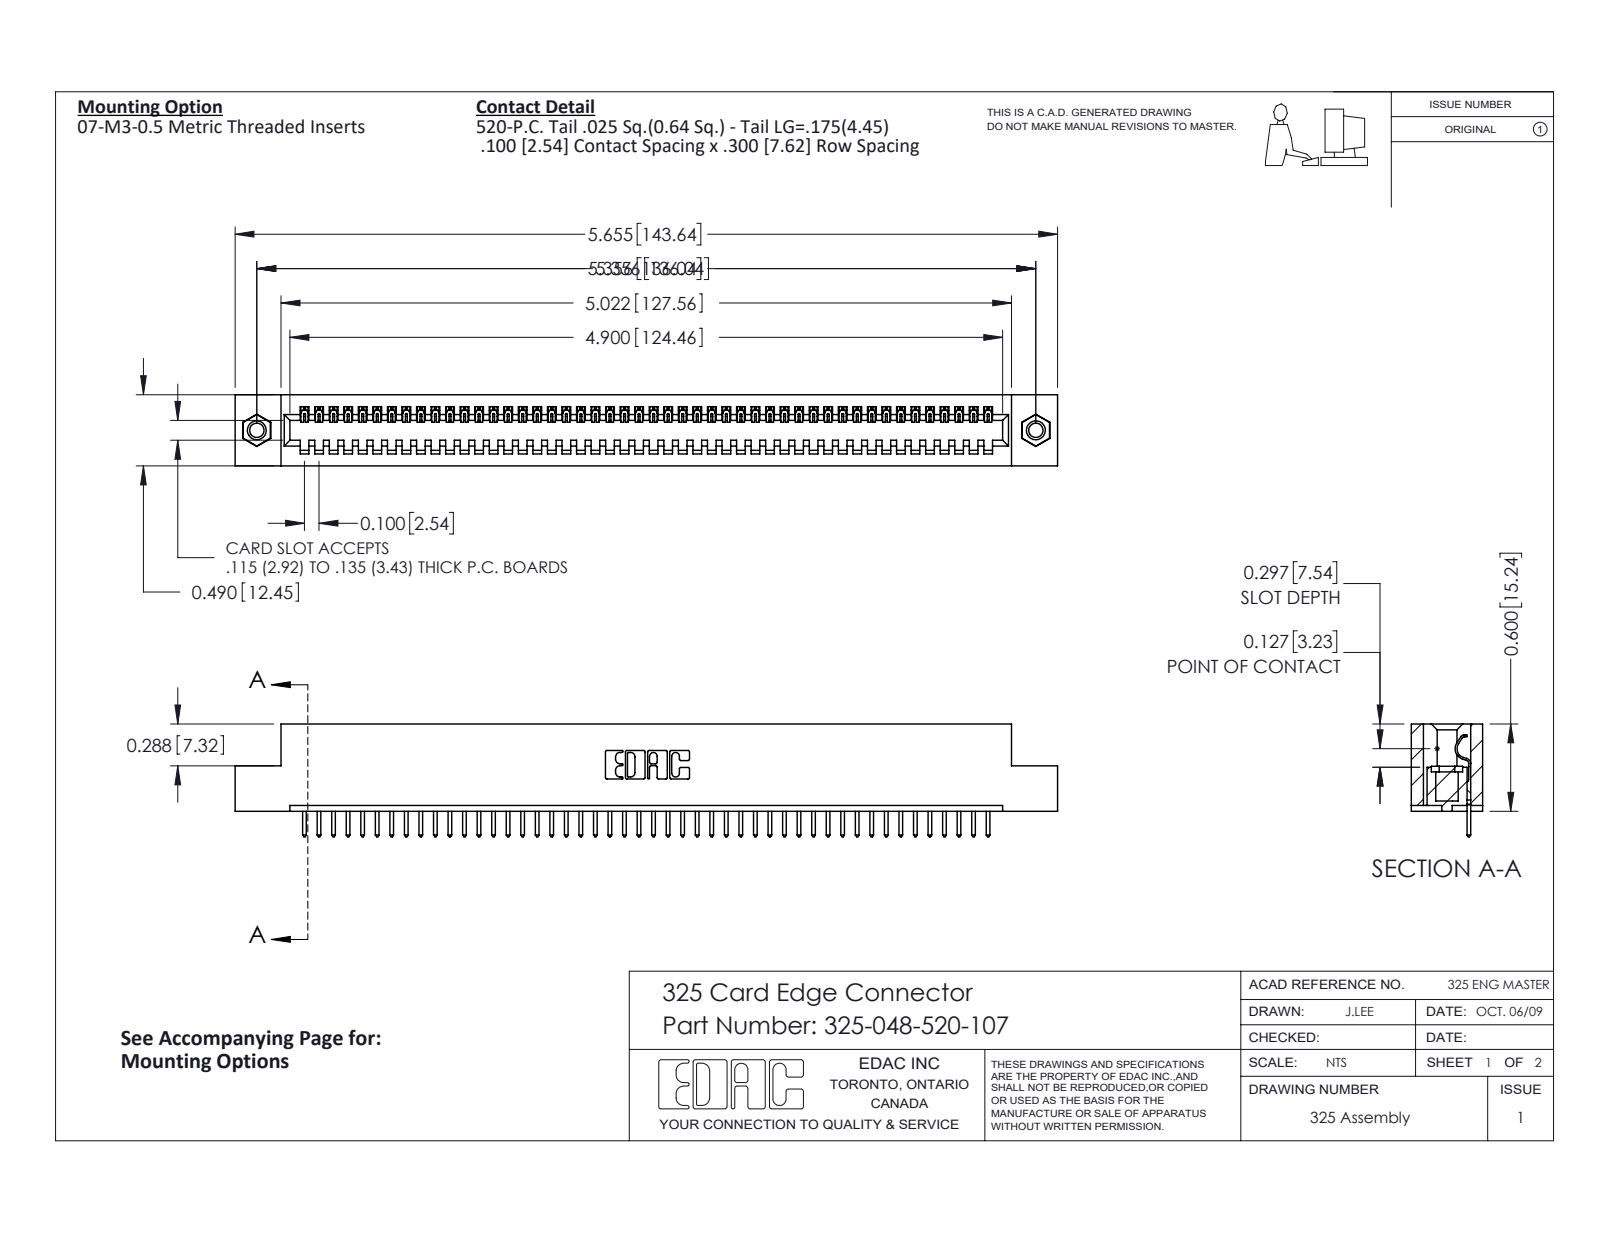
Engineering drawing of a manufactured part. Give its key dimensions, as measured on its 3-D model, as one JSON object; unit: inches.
{"part_name": "325-292-001_325-293-120; 325 Part_TI; 325-048-520-107; 345-250-001_345-250-005-103", "step_written_by": "SolidWorks 2016 (CONFIG_CONTROL_DESIGN)", "units": "inches", "bodies": {"solids": 51, "faces": 2958, "planar": 2118, "cylindrical": 824, "other": 16}, "overall_size": [5.655, 0.775, 0.49], "volume_in3": 1.107, "surface_area_in2": 30.14, "round_holes": [[0.098, 2], [0.125, 2], [0.16, 2]], "round_bosses_or_shafts": [[0.155, 2]], "partial_cylinders_radius": [[0.006, 96], [0.01, 96], [0.01, 22], [0.007, 6], [0.031, 6], [0.026, 3], [0.014, 1], [0.022, 1]], "face_to_face_distances": [0.083, 0.407, 0.49, 0.3, 0.107, 0.383, 0.025, 0.325, 0.56, 0.263], "hole_center_spacings": [5.356]}
